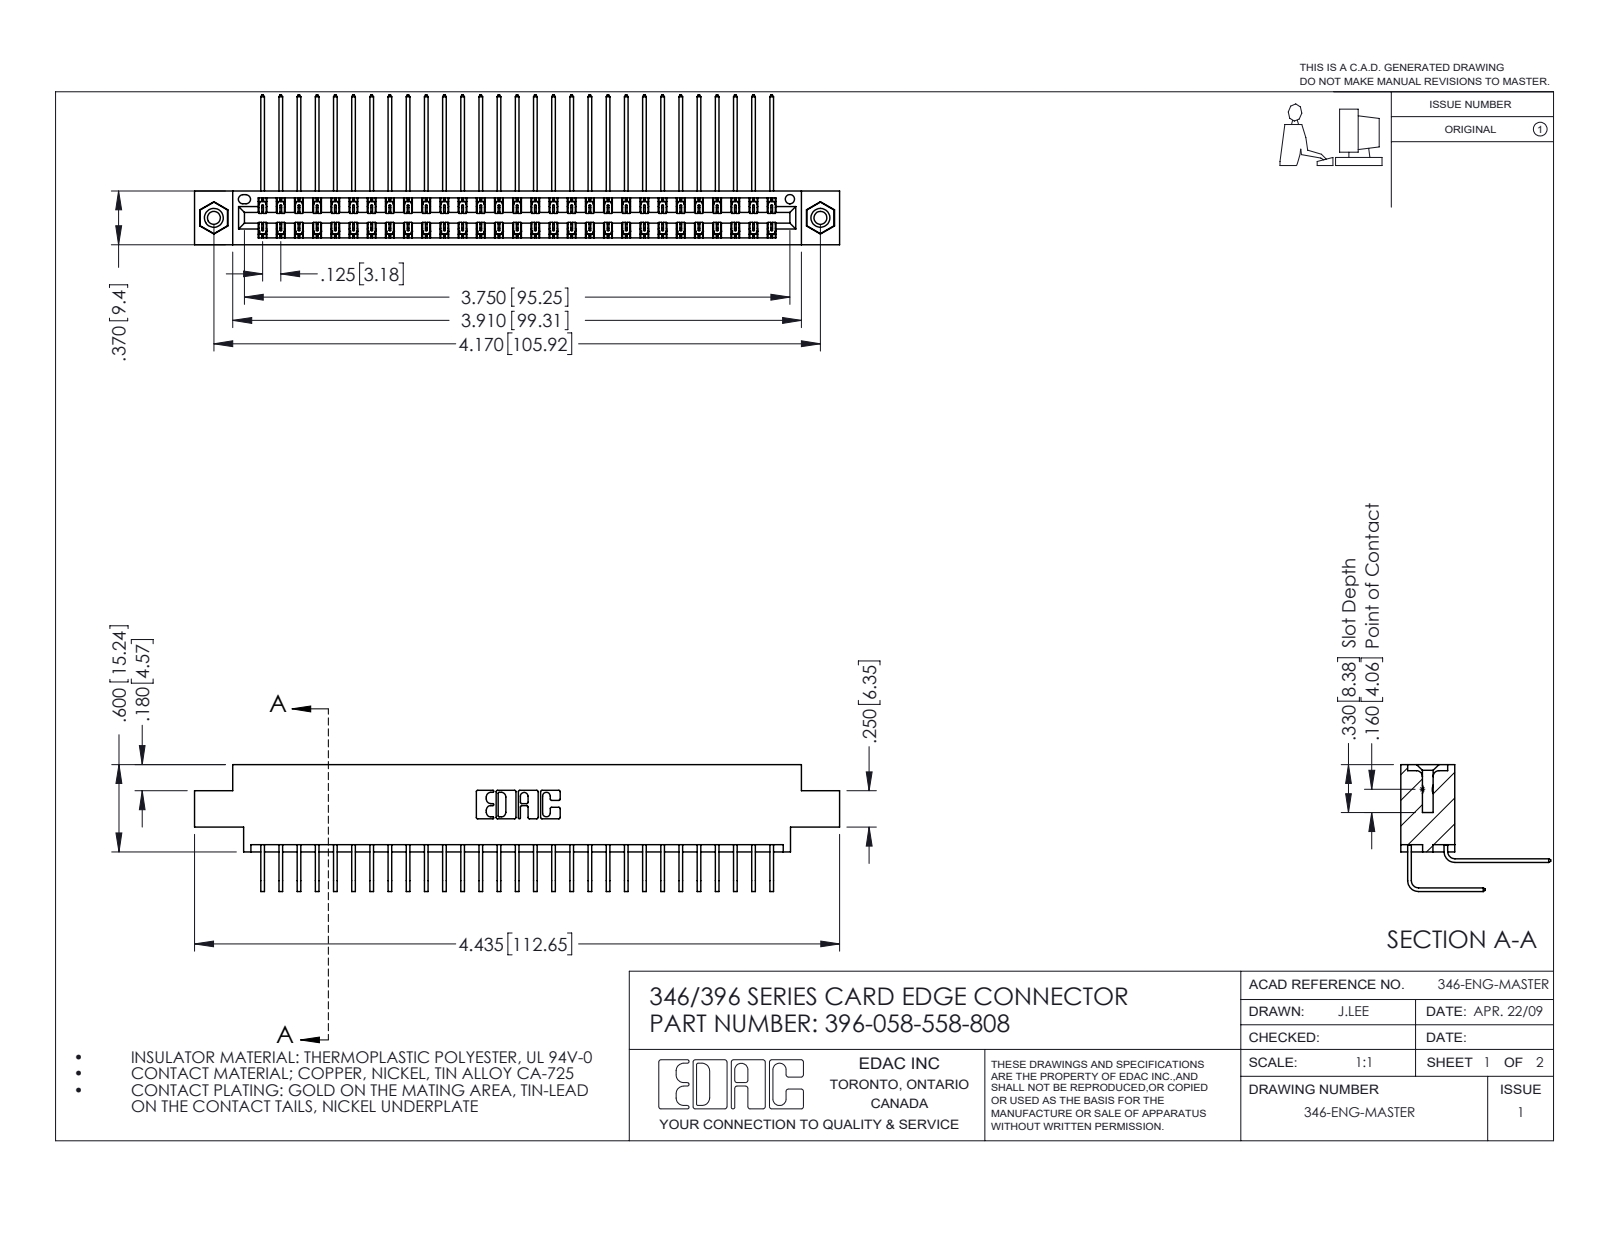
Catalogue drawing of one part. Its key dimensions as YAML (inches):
part_name: "345-250-001_345-250-003-102; 396-058-558-808; 345-292-001_558 559 Tail - 1; 346 Part_0.170 Offset - 0.156 Dia-TI (+1 more)"
step_written_by: "SolidWorks 2016 (CONFIG_CONTROL_DESIGN)"
units: inches
bodies: {solids: 61, faces: 3318, planar: 2258, cylindrical: 1044, other: 16}
overall_size: [4.435, 1.03, 0.873]
volume: 0.675
surface_area: 26.04
round_holes:
  - {diameter: 0.089, count: 2}
  - {diameter: 0.125, count: 2}
  - {diameter: 0.156, count: 2}
  - {diameter: 0.064, count: 1}
round_bosses_or_shafts:
  - {diameter: 0.155, count: 2}
partial_cylinders:
  - {radius: 0.006, count: 87}
  - {radius: 0.01, count: 22}
  - {radius: 0.007, count: 6}
  - {radius: 0.031, count: 6}
  - {radius: 0.026, count: 3}
  - {radius: 0.014, count: 2}
  - {radius: 0.022, count: 2}
  - {radius: 0.024, count: 2}
face_to_face_distances: [0.322, 0.048, 0.025, 0.37, 0.25, 0.298, 0.072, 0.275, 0.222, 0.148]
hole_center_spacings: [0.246, 3.962, 4.17]
